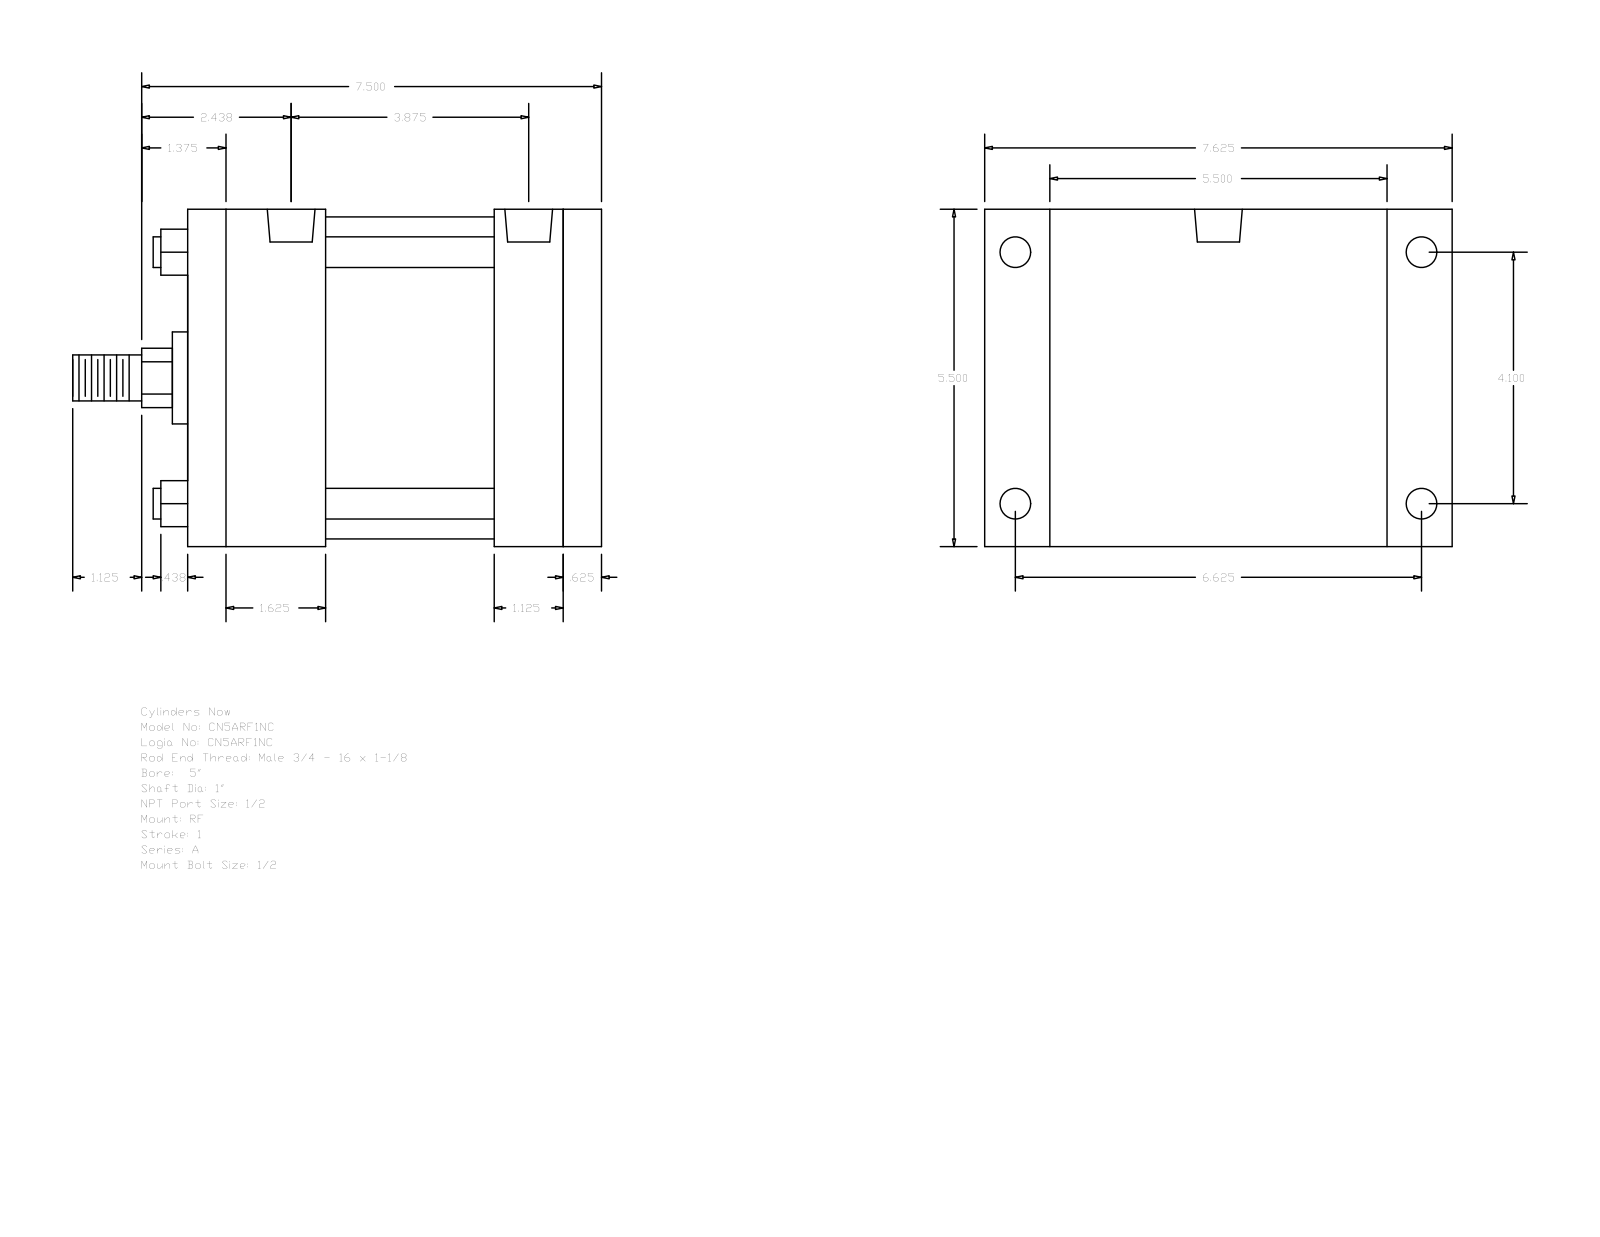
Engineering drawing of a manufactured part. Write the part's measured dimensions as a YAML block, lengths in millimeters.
part_name: "A_RF__0500_1"
step_written_by: "GSSL Pune (CONFIG_CONTROL_DESIGN)"
units: millimeters
bodies: {solids: 0, faces: 92, planar: 64, cylindrical: 28, other: 0}
overall_size: [219.07, 193.68, 139.7]
round_holes:
  - {diameter: 8.73, count: 4}
  - {diameter: 12.7, count: 4}
  - {diameter: 19.77, count: 2}
round_bosses_or_shafts:
  - {diameter: 12.7, count: 4}
  - {diameter: 133.35, count: 1}
  - {diameter: 38.1, count: 1}
  - {diameter: 25.4, count: 1}
  - {diameter: 19.05, count: 1}
partial_cylinders:
  - {radius: 12.29, count: 1}
face_to_face_distances: [139.7, 171.45, 155.57, 15.88, 28.57, 57.15, 98.42, 114.3, 127, 69.85]
hole_center_spacings: [2.39, 93.65, 96.04, 104.14, 168.28, 197.9, 98.43]
